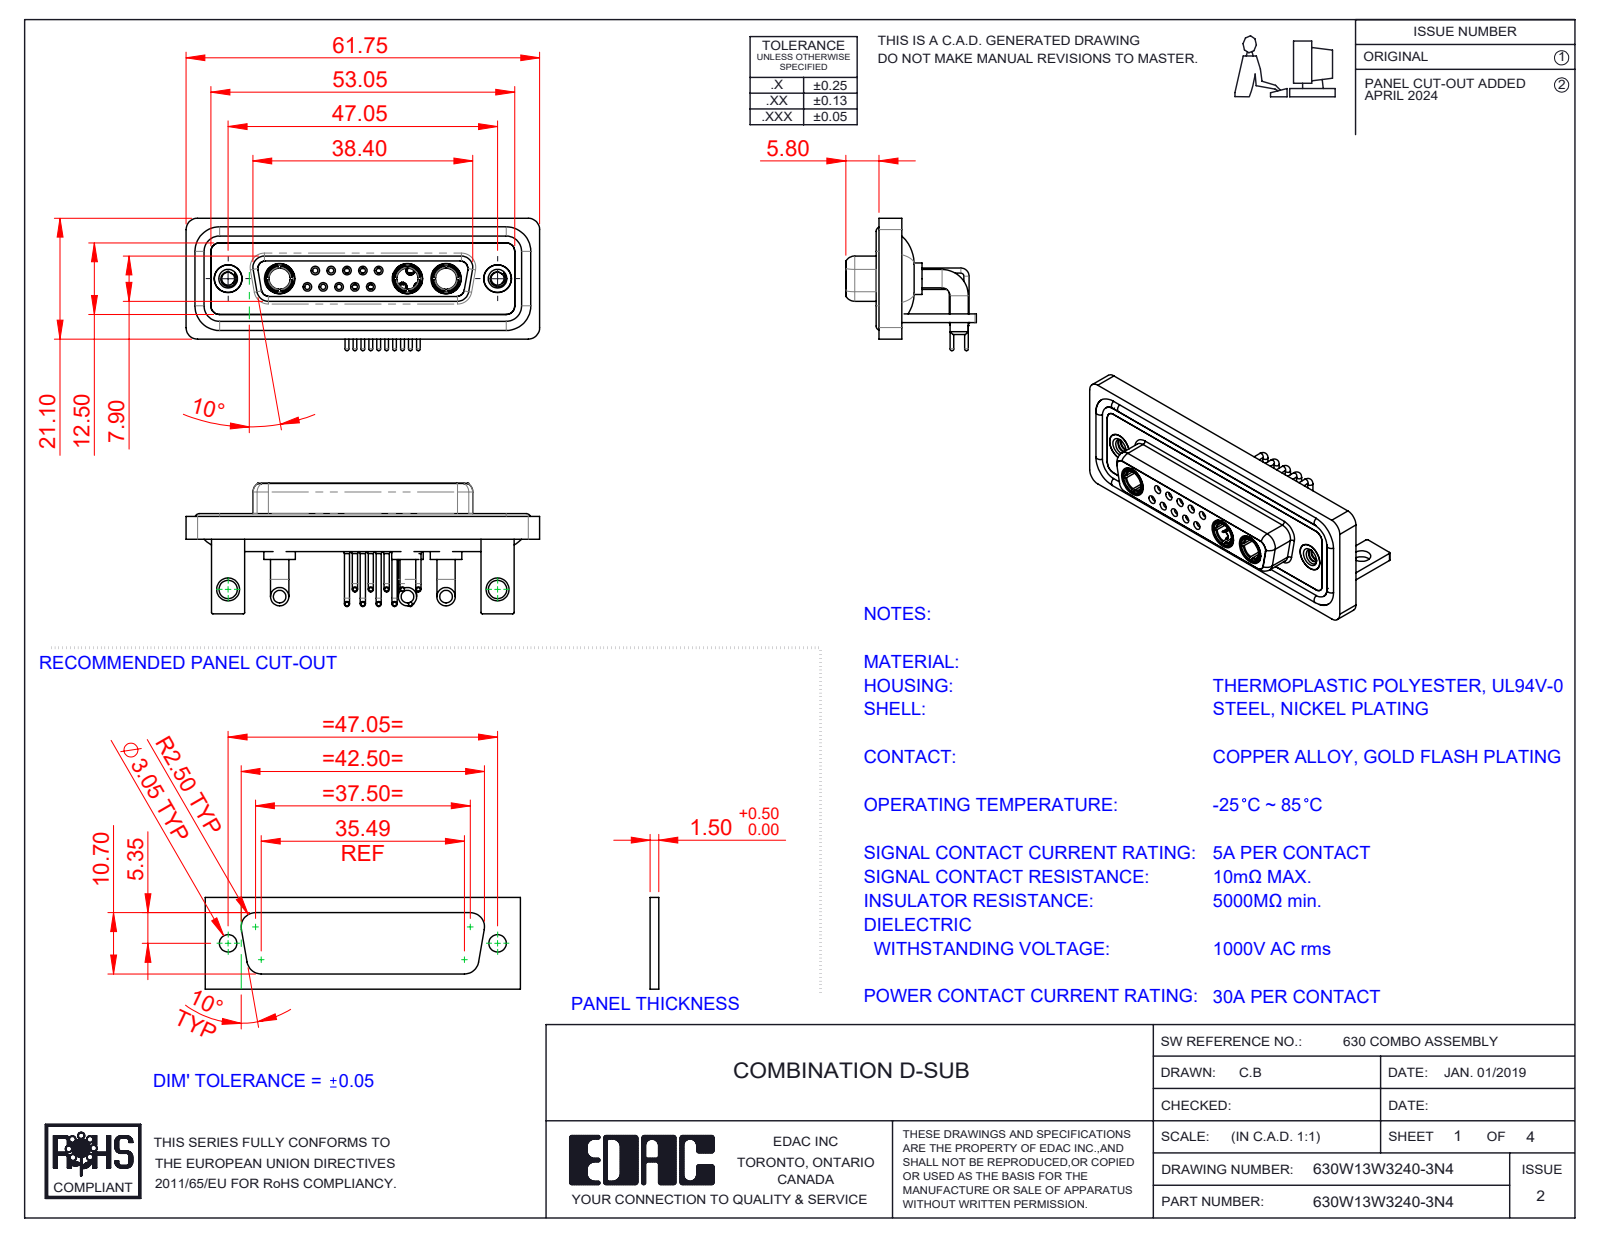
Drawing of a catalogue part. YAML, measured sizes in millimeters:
part_name: "630Combo Contact Row 1_50 Contacts; 630Combo Waterproof Housing_25 Contacts; Power Socket_30A RA; 630Combo Stabilizer Bracket_50 Contacts (+6 more)"
step_written_by: "SolidWorks 2023 (CONFIG_CONTROL_DESIGN)"
units: millimeters
bodies: {solids: 25, faces: 1198, planar: 362, cylindrical: 517, other: 319}
overall_size: [61.75, 23.12, 22.8]
volume: 8921
surface_area: 15087
round_holes:
  - {diameter: 0.9, count: 10}
  - {diameter: 1.1, count: 10}
  - {diameter: 1.5, count: 10}
  - {diameter: 2, count: 10}
  - {diameter: 1.6, count: 5}
  - {diameter: 1.7, count: 5}
  - {diameter: 4.85, count: 5}
  - {diameter: 3.7, count: 3}
  - {diameter: 5.3, count: 3}
  - {diameter: 2.26, count: 2}
  - {diameter: 3.2, count: 2}
  - {diameter: 4, count: 2}
round_bosses_or_shafts:
  - {diameter: 0.9, count: 15}
  - {diameter: 1.6, count: 12}
  - {diameter: 0.65, count: 10}
  - {diameter: 3.2, count: 6}
  - {diameter: 2, count: 5}
  - {diameter: 1.5, count: 5}
  - {diameter: 5.5, count: 3}
  - {diameter: 5.2, count: 3}
partial_cylinders:
  - {radius: 2, count: 19}
  - {radius: 1.5, count: 18}
  - {radius: 0.25, count: 16}
  - {radius: 1.35, count: 8}
  - {radius: 1.6, count: 8}
  - {radius: 0.5, count: 5}
  - {radius: 0.6, count: 4}
  - {radius: 0.65, count: 4}
face_to_face_distances: [0.4, 1.8, 2.9, 3.7, 1.5, 4.1, 1.1, 1.4, 1.6, 3.1]
hole_center_spacings: [3.16, 2.77, 5.54, 5.04, 8.31, 5.03, 7.49, 11.08]
